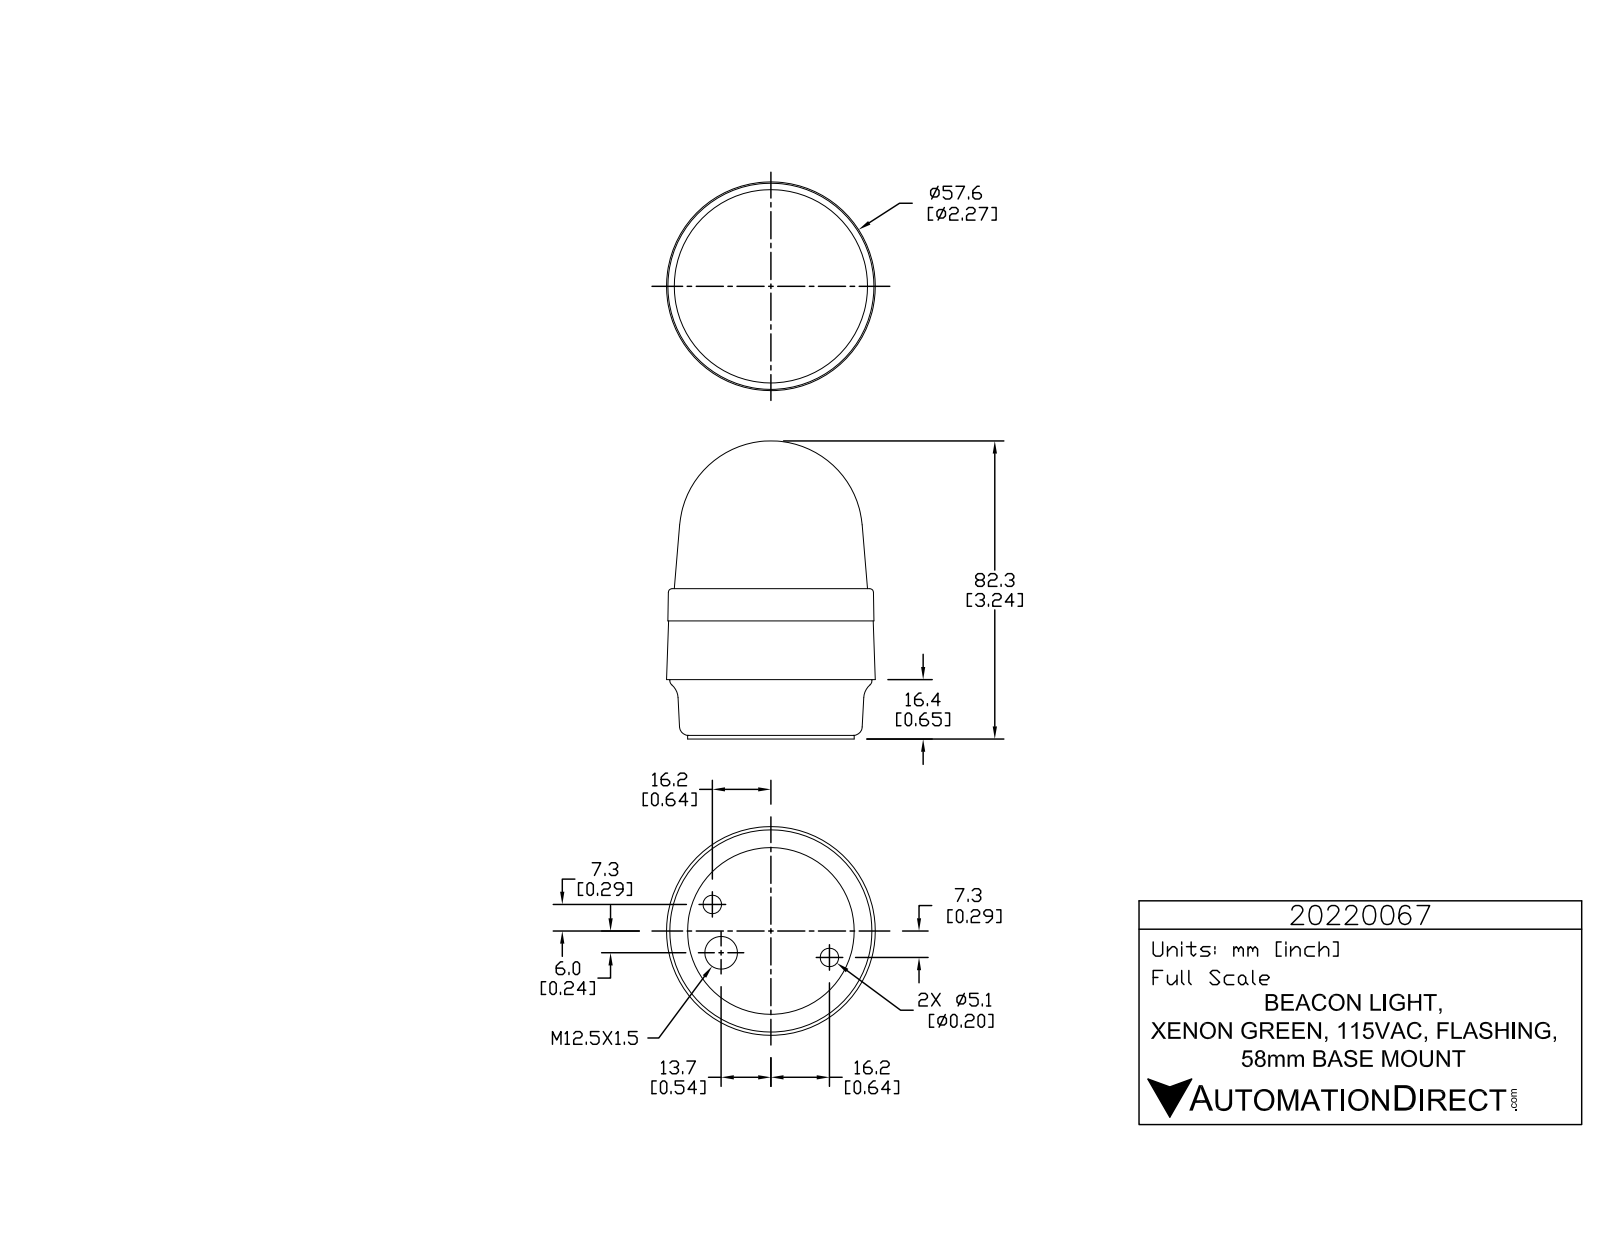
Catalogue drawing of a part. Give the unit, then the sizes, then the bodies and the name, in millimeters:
Units: millimetres
Overall size (bounding box): 82.3 × 57.63 × 57.63
Round holes (diameter × count): ⌀0.99 ×3, ⌀5.11 ×2, ⌀9 ×1
Round bosses / shafts (diameter × count): ⌀5.74 ×3, ⌀1.43 ×3, ⌀55.8 ×1, ⌀46 ×1
Partial cylindrical surfaces — rounded edges, fillets, slot ends (radius × count): R0.2 ×6, R0.21 ×6, R0.21 ×6, R3.32 ×6, R0.1 ×3, R0.12 ×3, R0.19 ×3, R0.2 ×3
Main face-to-face distances: 16.4, 1, 15.4, 41.5, 40.5, 25.1, 32.6, 31.6, 16.2, 8.9
Hole centre spacings: 13.56, 29.94, 35.5
Volume: 164 395 mm³ · Surface area: 16 261 mm²
Bodies: 1 solid, 763 faces (527 planar, 145 cylindrical, 91 other)
Part name (STEP PRODUCT): 20220067
STEP written by: SolidWorks 2015 (AUTOMOTIVE_DESIGN)
